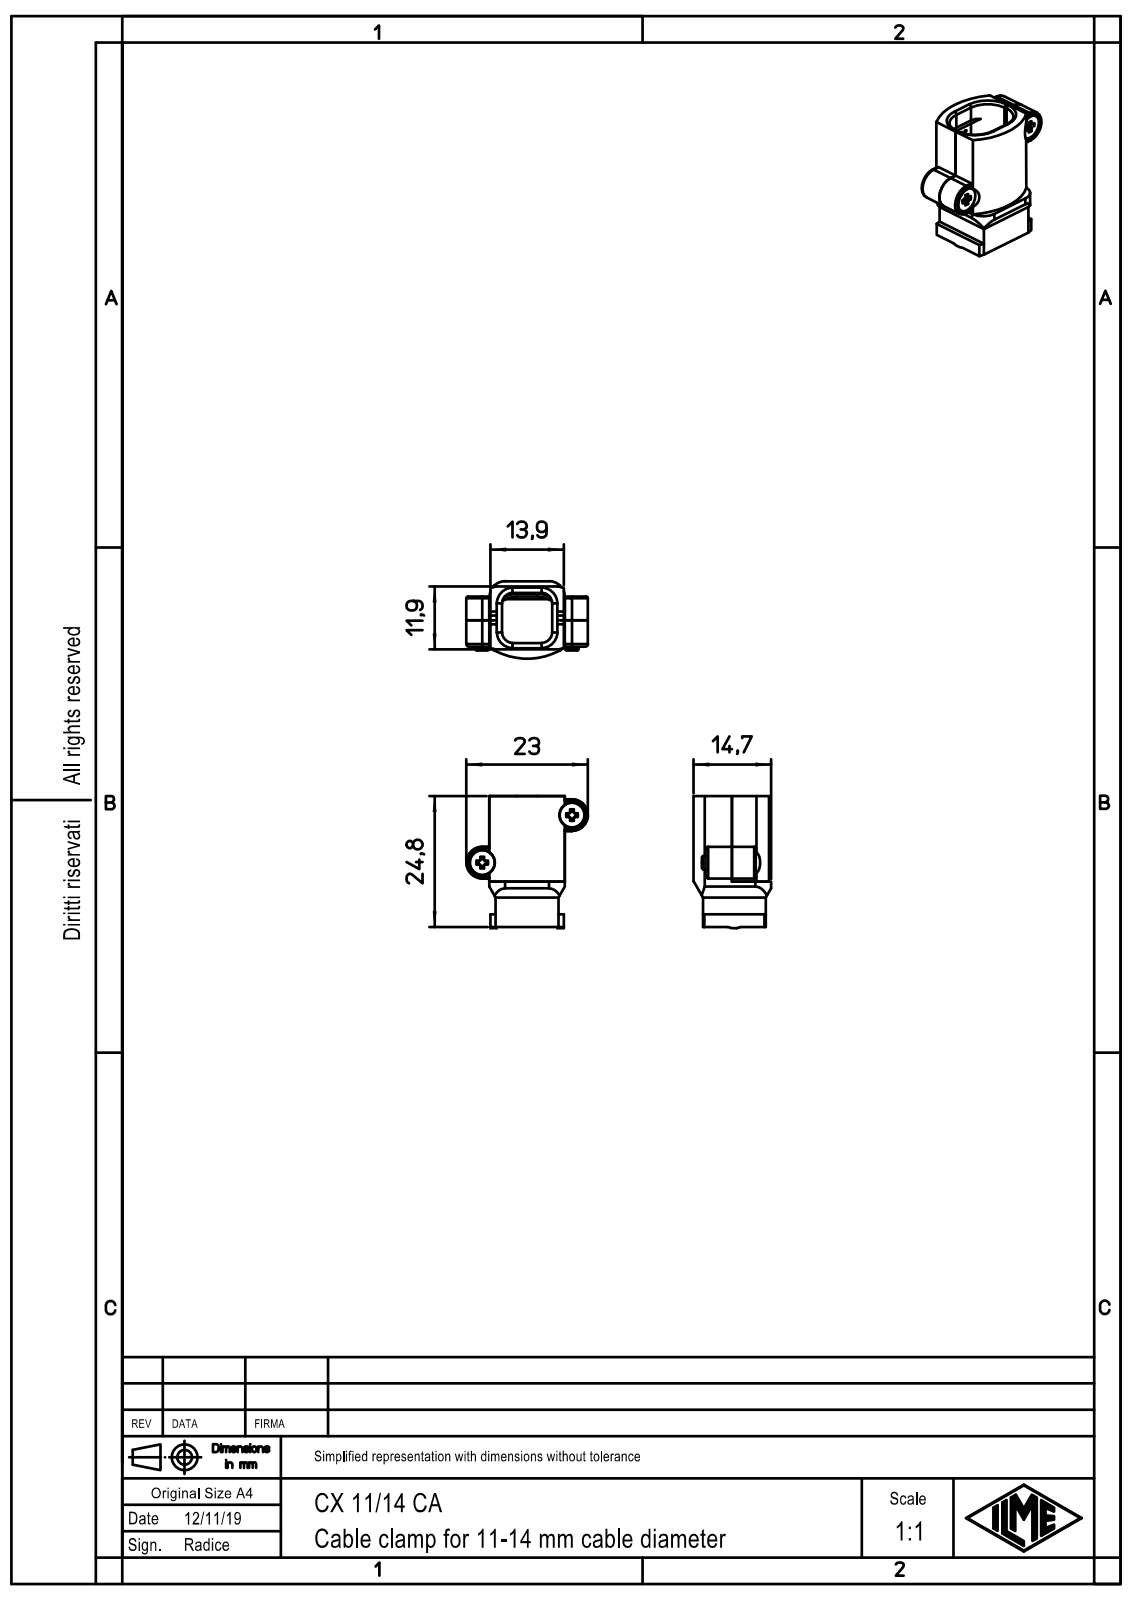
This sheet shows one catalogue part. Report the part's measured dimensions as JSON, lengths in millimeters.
{"part_name": "Serracavo_CX1114CA; Vite_M2.5_CX1114CA.1; Collarino_CX1114CA; CX_11-14_CA", "step_written_by": "Creo Elements/Direct Modeling 20.1B 02-Apr-2019 (C) Parametric Technology GmbH (AUTOMOTIVE_DESIGN)", "units": "millimeters", "bodies": {"solids": 4, "faces": 262, "planar": 137, "cylindrical": 73, "other": 52}, "overall_size": [25, 23, 14.7], "volume_mm3": 2322, "surface_area_mm2": 3101, "round_holes": [[2.15, 2], [2.6, 2], [4.8, 2]], "round_bosses_or_shafts": [[4.7, 2], [2.5, 2], [2.3, 2]], "partial_cylinders_radius": [[0.5, 9], [0.3, 4], [1, 4], [2, 4], [3, 4], [4.5, 4], [12, 1], [13, 1]], "face_to_face_distances": [1.2, 11.9, 10.7, 9.5, 14.3, 0.7, 2.4, 0.5, 13.1, 12.9], "hole_center_spacings": [19.24]}
